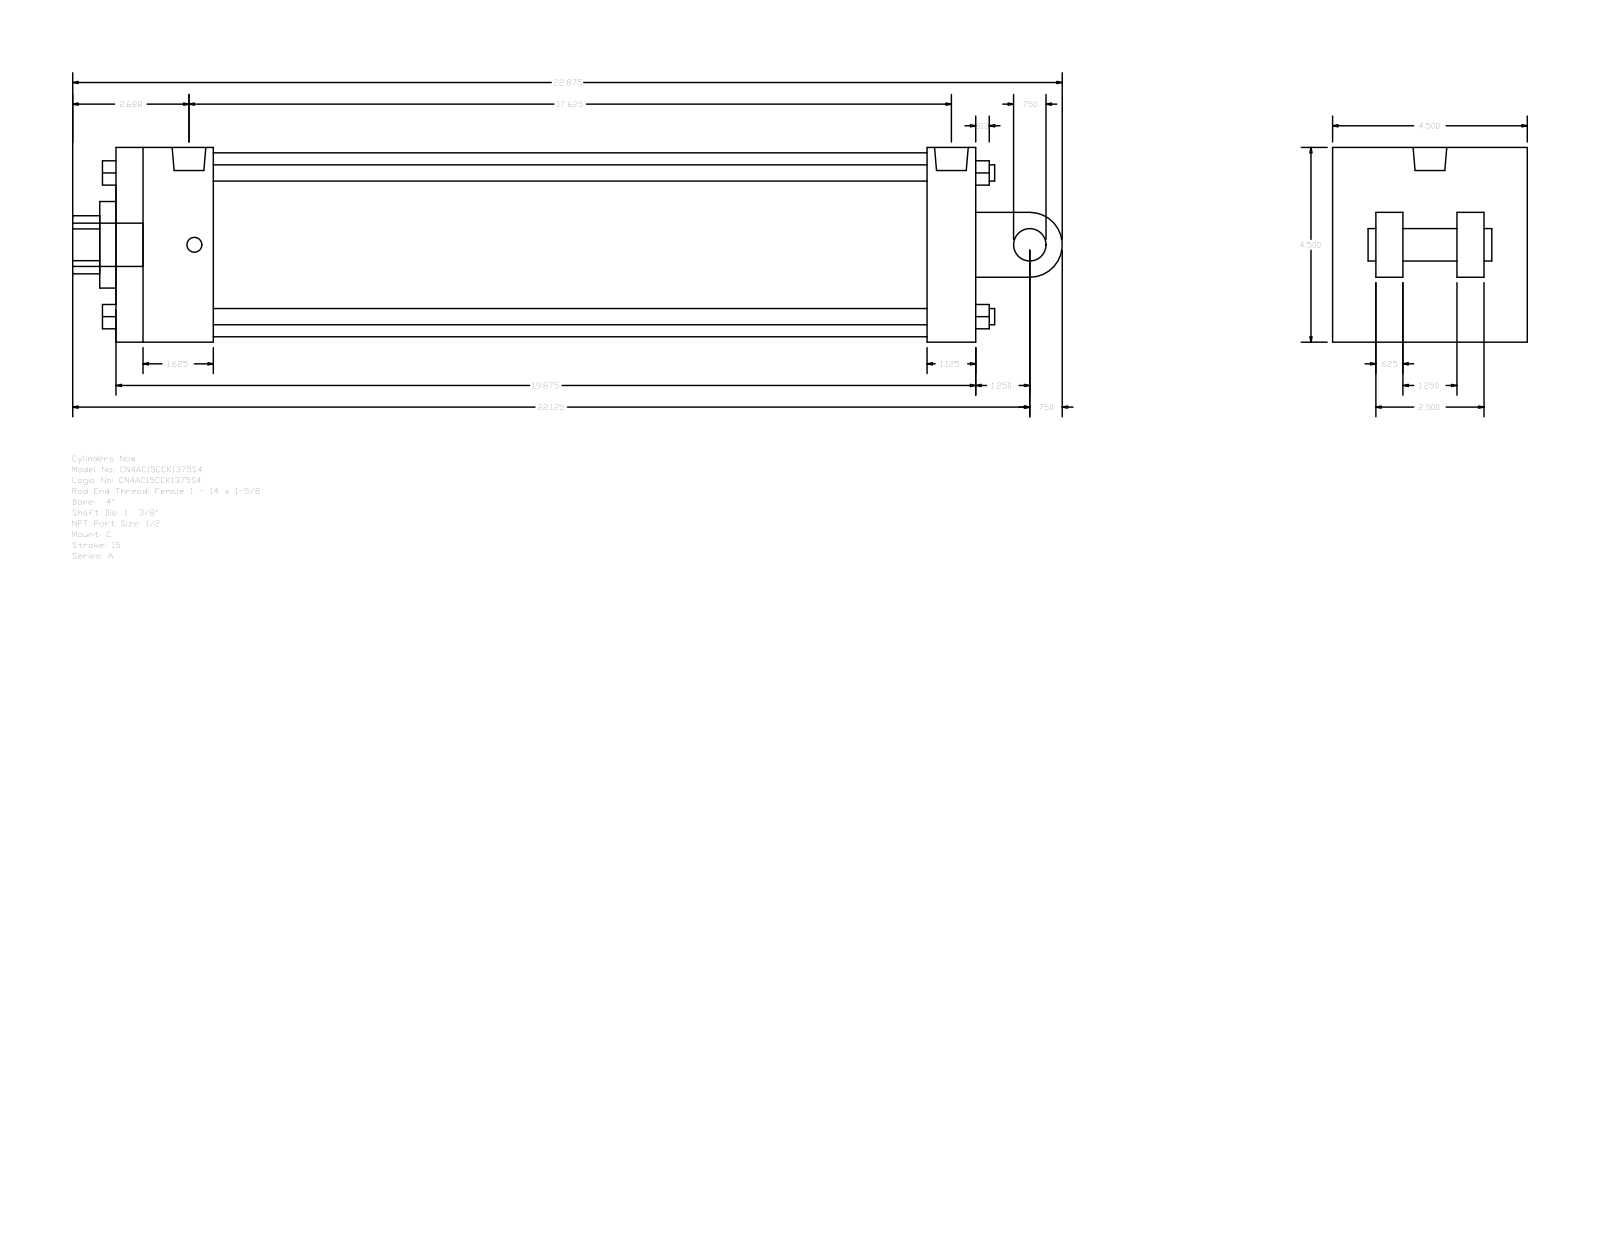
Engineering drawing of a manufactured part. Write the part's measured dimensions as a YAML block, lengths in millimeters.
part_name: "A_C__0400_1.375"
step_written_by: "GSSL Pune (CONFIG_CONTROL_DESIGN)"
units: millimeters
bodies: {solids: 0, faces: 135, planar: 102, cylindrical: 33, other: 0}
overall_size: [581.02, 114.3, 114.3]
round_holes:
  - {diameter: 8.73, count: 2}
  - {diameter: 19.77, count: 1}
  - {diameter: 34.92, count: 1}
  - {diameter: 50.8, count: 1}
  - {diameter: 107.95, count: 1}
round_bosses_or_shafts:
  - {diameter: 9.53, count: 4}
  - {diameter: 8.73, count: 2}
  - {diameter: 25.4, count: 1}
  - {diameter: 19.77, count: 1}
  - {diameter: 19.05, count: 1}
partial_cylinders:
  - {radius: 17.06, count: 1}
  - {radius: 19.05, count: 1}
face_to_face_distances: [114.3, 504.83, 28.58, 73.03, 476.25, 57.15, 419.1, 447.68, 15.87, 41.27]
hole_center_spacings: [3.18]
